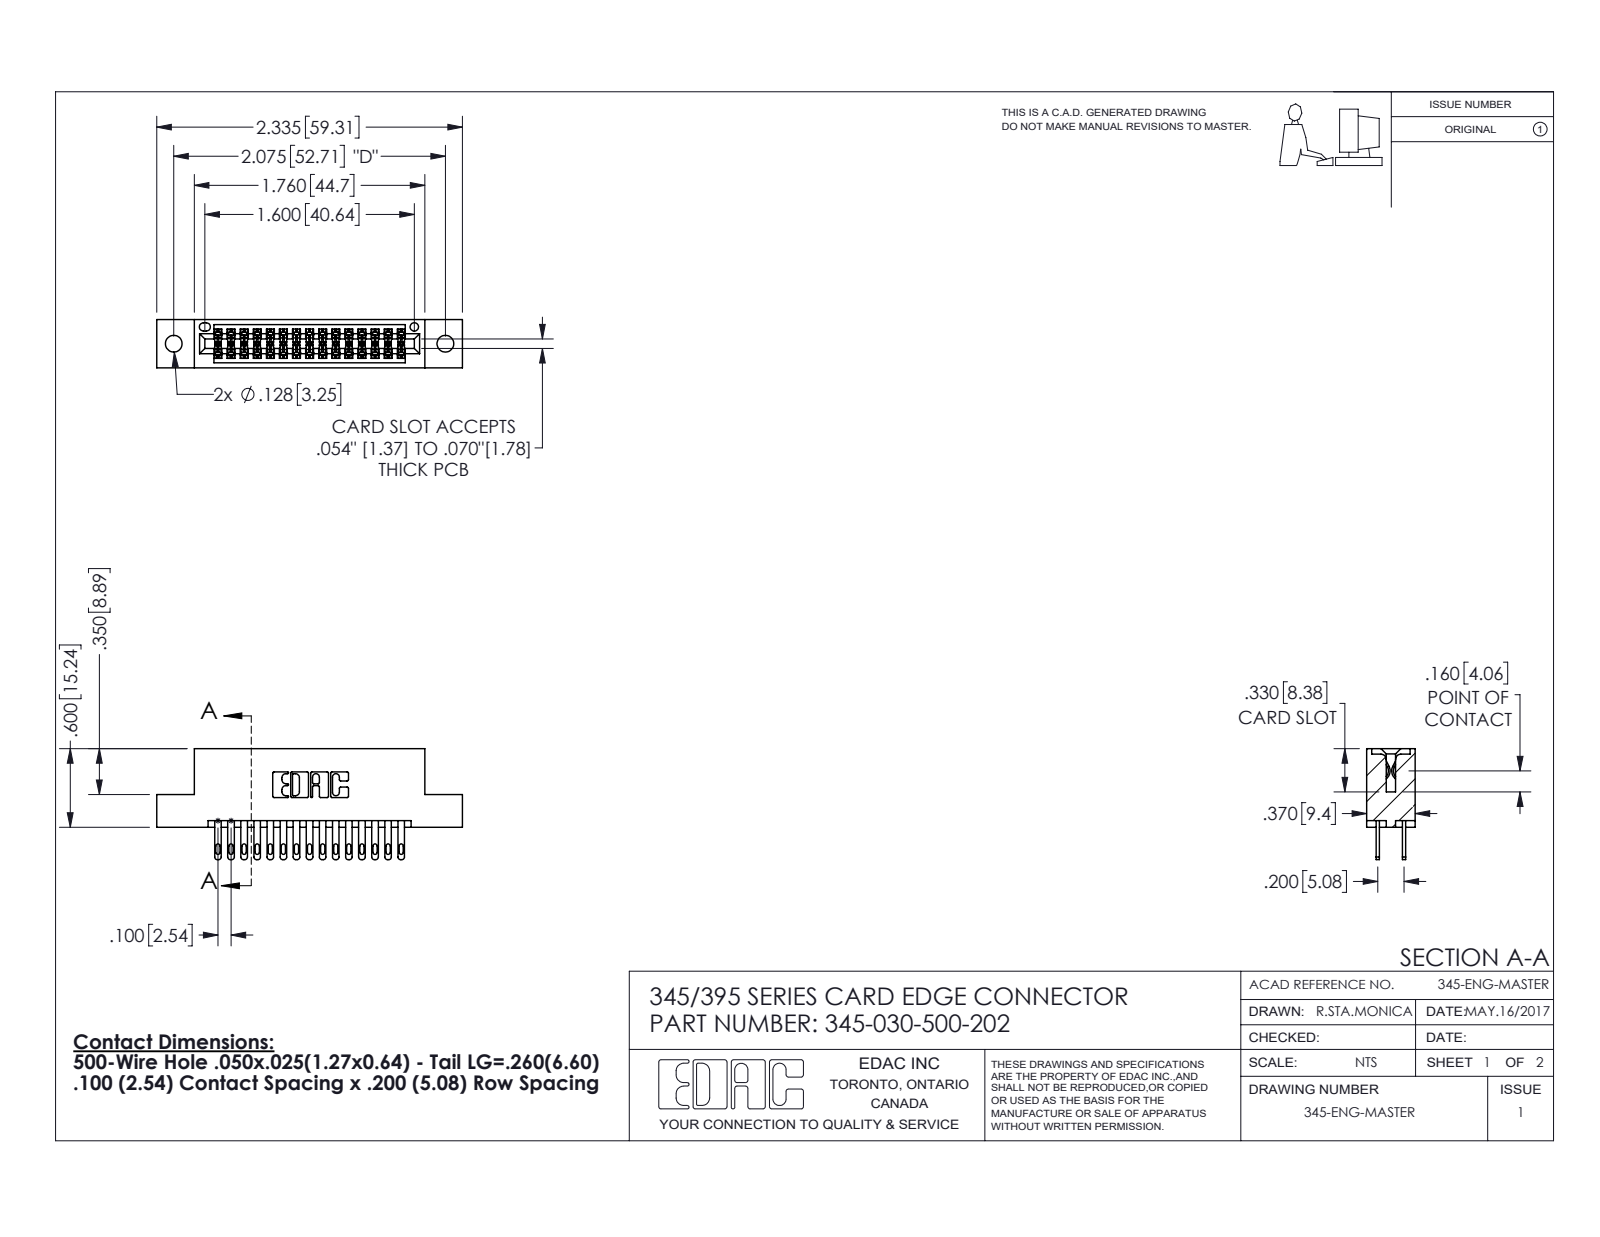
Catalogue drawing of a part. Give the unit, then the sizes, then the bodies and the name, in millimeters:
Units: millimetres
Overall size (bounding box): 59.3 × 21.5 × 9.4
Round holes (diameter × count): ⌀3.3 ×2, ⌀1.6 ×1
Partial cylindrical surfaces — rounded edges, fillets, slot ends (radius × count): R0.2 ×45, R0.4 ×30, R0.5 ×30, R0.3 ×22, R0.2 ×6, R0.8 ×6, R0.7 ×3, R0.4 ×2
Main face-to-face distances: 7.6, 1.8, 5.1, 2.5, 6.9, 0.6, 9.4, 5.7, 4.4, 2.5
Hole centre spacings: 6.9, 46.8, 52.7
Volume: 5 570 mm³ · Surface area: 7 735 mm²
Bodies: 31 solids, 1506 faces (890 planar, 616 cylindrical, 0 other)
Part name (STEP PRODUCT): 345-030-500-202; 345-292-001_345-293-100; 345 Part_Flush Mounting Lugs - 0.128 Dia
STEP written by: SolidWorks 2016 (CONFIG_CONTROL_DESIGN)
